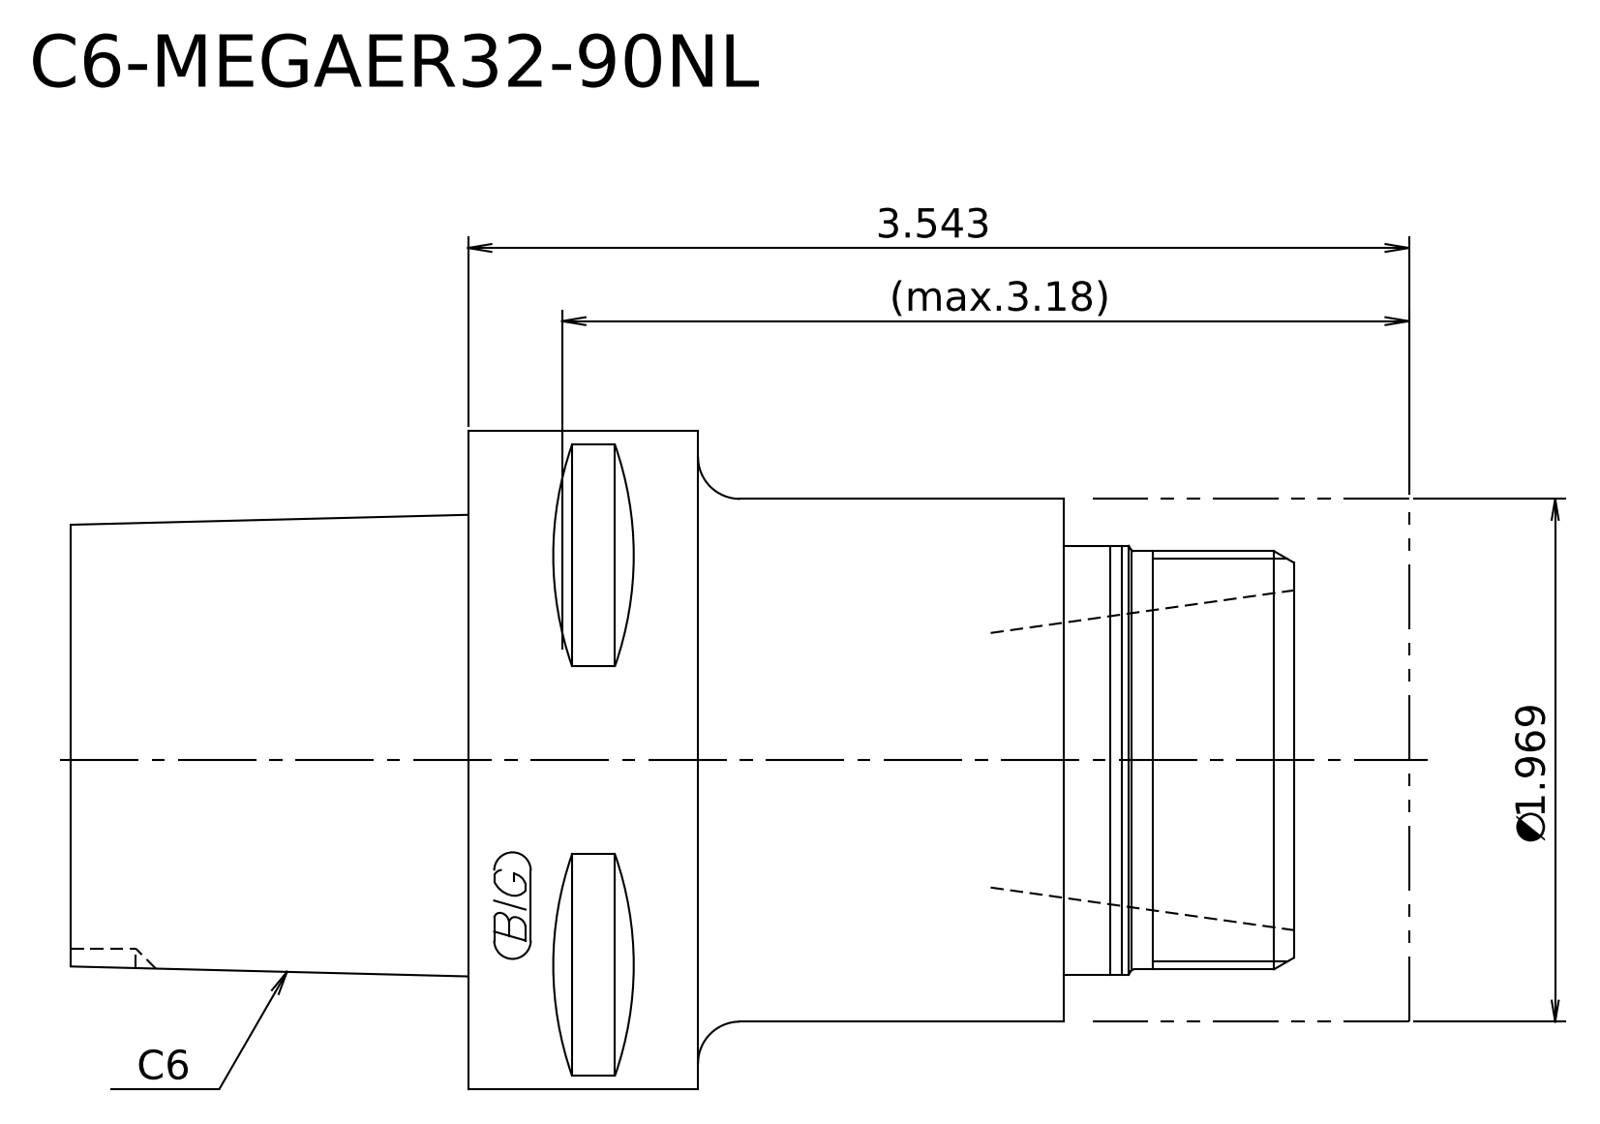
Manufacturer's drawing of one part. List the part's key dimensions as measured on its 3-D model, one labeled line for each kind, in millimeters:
STEP written by: Kubotek KeyCreator 2011 V10.0.2 (22737) (automotive_design)
Units: millimetres
Bodies: 2 solids, 18 faces (7 planar, 5 cylindrical, 6 other)
Overall size (bounding box): 128 × 63 × 63
Volume: 280 633 mm³ · Surface area: 32 092 mm²
Round bosses / shafts (diameter × count): ⌀63 ×1, ⌀50 ×1, ⌀41 ×1, ⌀40 ×1
Main face-to-face distances: 30.2, 90, 59.8, 128, 97.8, 38, 11, 19.2, 79, 117
